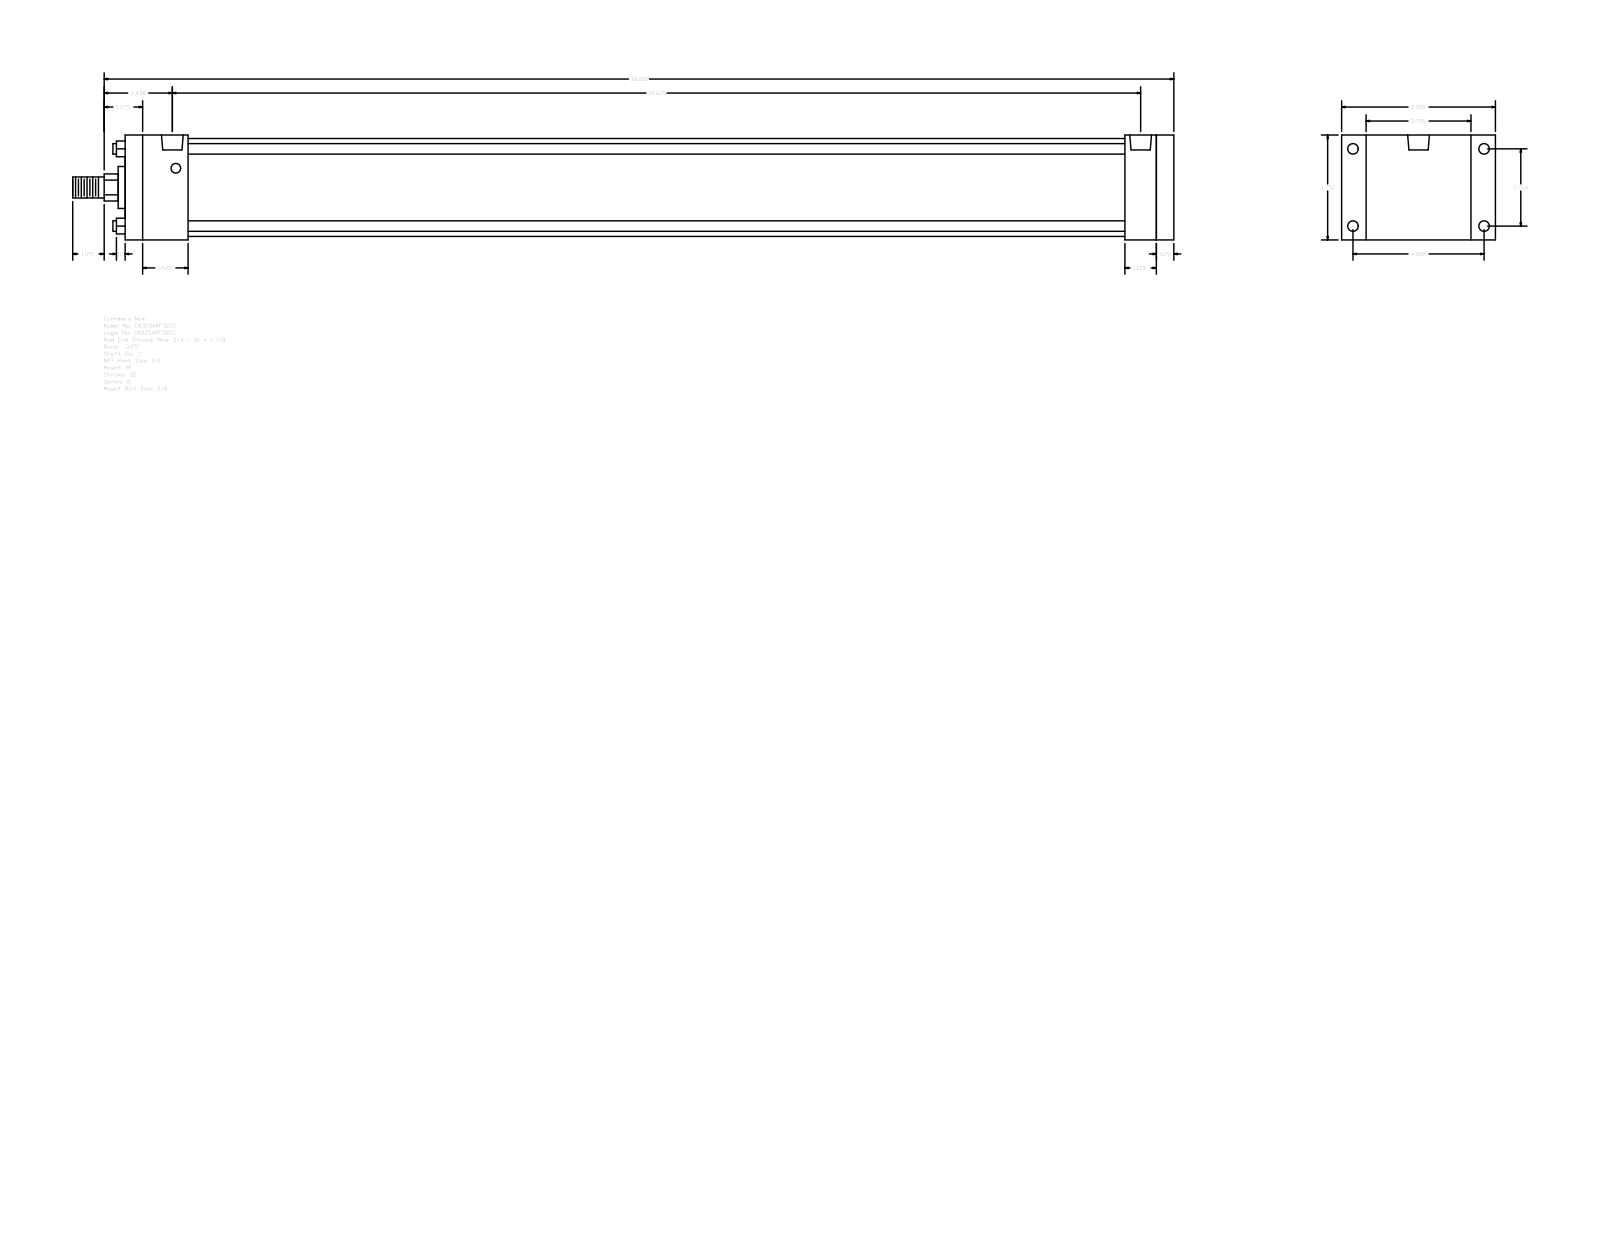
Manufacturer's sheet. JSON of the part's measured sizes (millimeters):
{"part_name": "A_RF__0325_1", "step_written_by": "GSSL Pune (CONFIG_CONTROL_DESIGN)", "units": "millimeters", "bodies": {"solids": 0, "faces": 92, "planar": 64, "cylindrical": 28, "other": 0}, "overall_size": [1000.12, 139.7, 95.25], "round_holes": [[8.73, 4], [9.53, 4], [19.77, 2]], "round_bosses_or_shafts": [[9.53, 4], [88.9, 1], [38.1, 1], [25.4, 1], [19.05, 1]], "partial_cylinders_radius": [[12.29, 1]], "face_to_face_distances": [95.24, 952.5, 936.62, 15.88, 22.23, 117.47, 28.57, 908.05, 44.45, 57.15], "hole_center_spacings": [3.18, 70.1, 119.06, 138.16, 873.12, 876.3, 879.48]}
